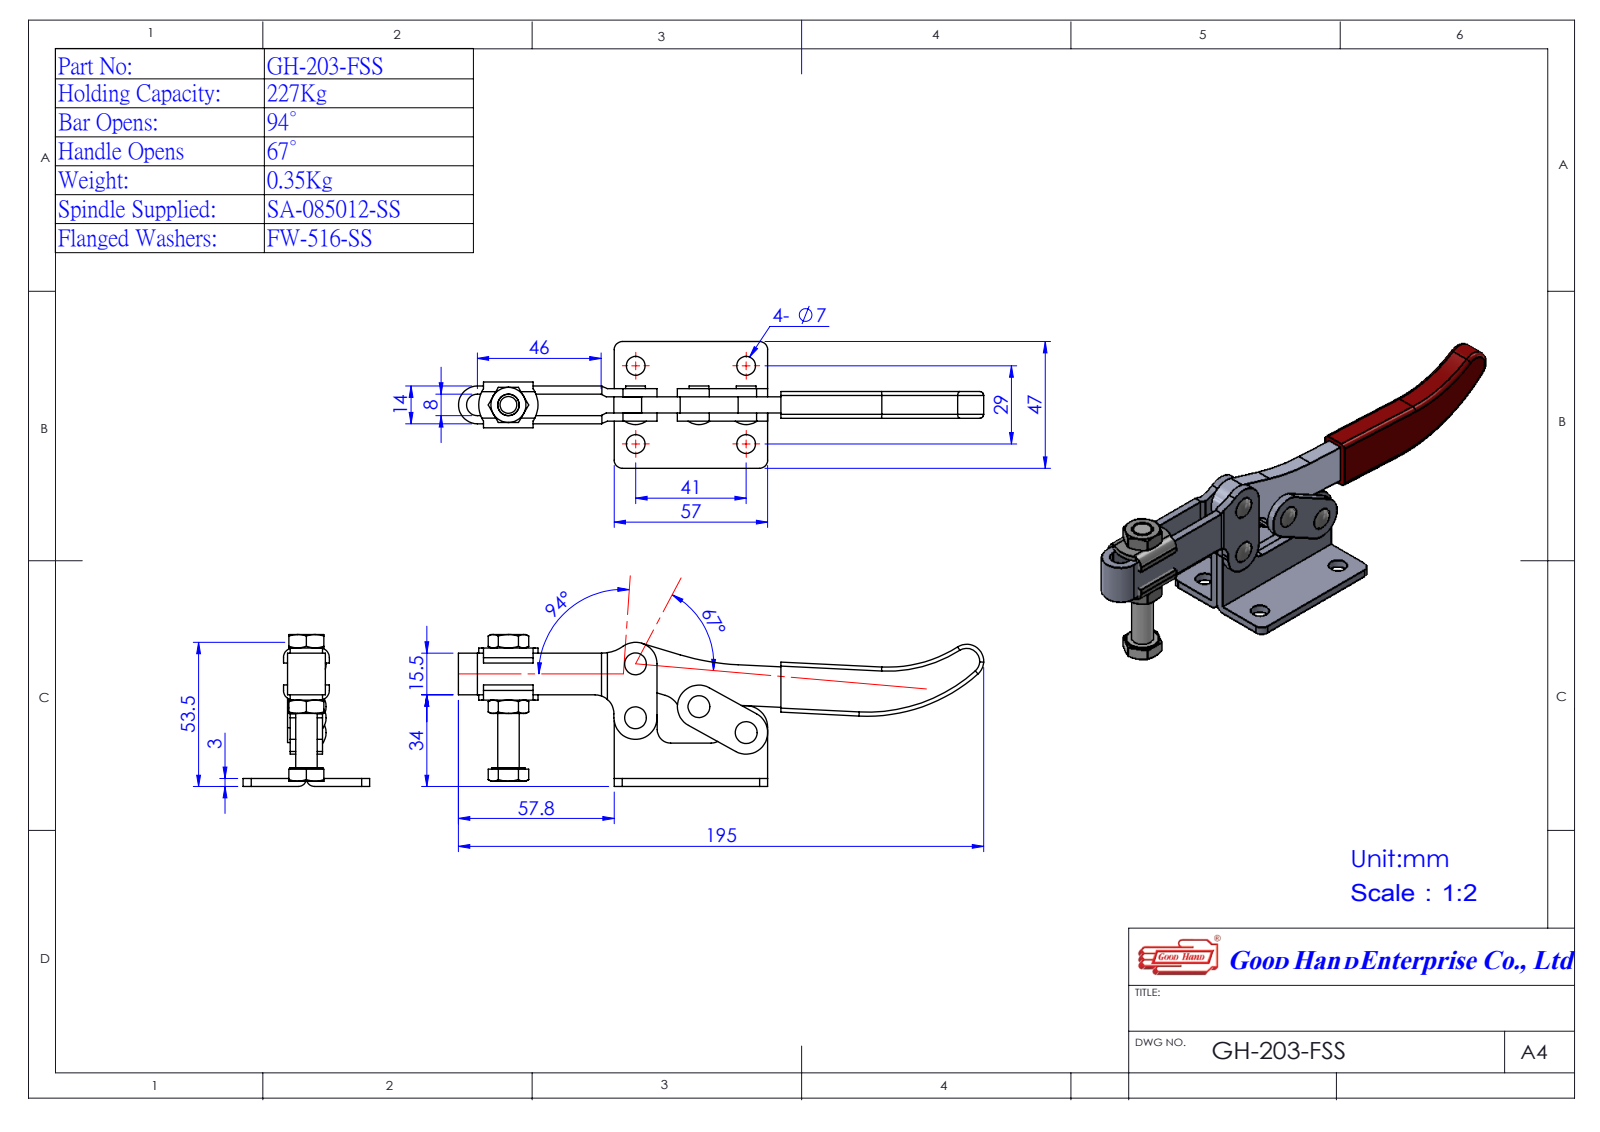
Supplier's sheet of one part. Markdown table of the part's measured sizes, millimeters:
| quantity | value |
| --- | --- |
| part name | 1203F01-1^GH-203-FSS(簡化)-1; Group4^GH-203-FSS(簡化)-1; Group5^GH-203-FSS(簡化); GH-203-FSS(簡化)-1 (+2 more) |
| STEP written by | SolidWorks 2016 (AUTOMOTIVE_DESIGN) |
| units | millimeters |
| bodies | 5 solids, 254 faces (115 planar, 101 cylindrical, 38 other) |
| overall size | 195 × 60.65 × 47 |
| volume | 51 786 mm³ |
| surface area | 30 094 mm² |
| round holes (diameter × count) | 5 × 4, 7 × 4, 6.33 × 1 |
| round bosses / shafts (diameter × count) | 7.35 × 4, 12.5 × 1, 8 × 1, 5 × 1 |
| partial cylindrical surfaces (radius × count) | 8 × 8, 1.2 × 4, 3 × 4, 3.6 × 4, 5 × 2, 7 × 2, 11.04 × 2, 4 × 1 |
| main face-to-face distances | 1, 2, 3, 10, 8, 11, 9, 6, 12, 13 |
| hole center spacings | 20, 29, 41, 50.22, 23.84, 28.4, 41.37, 48.35 |
